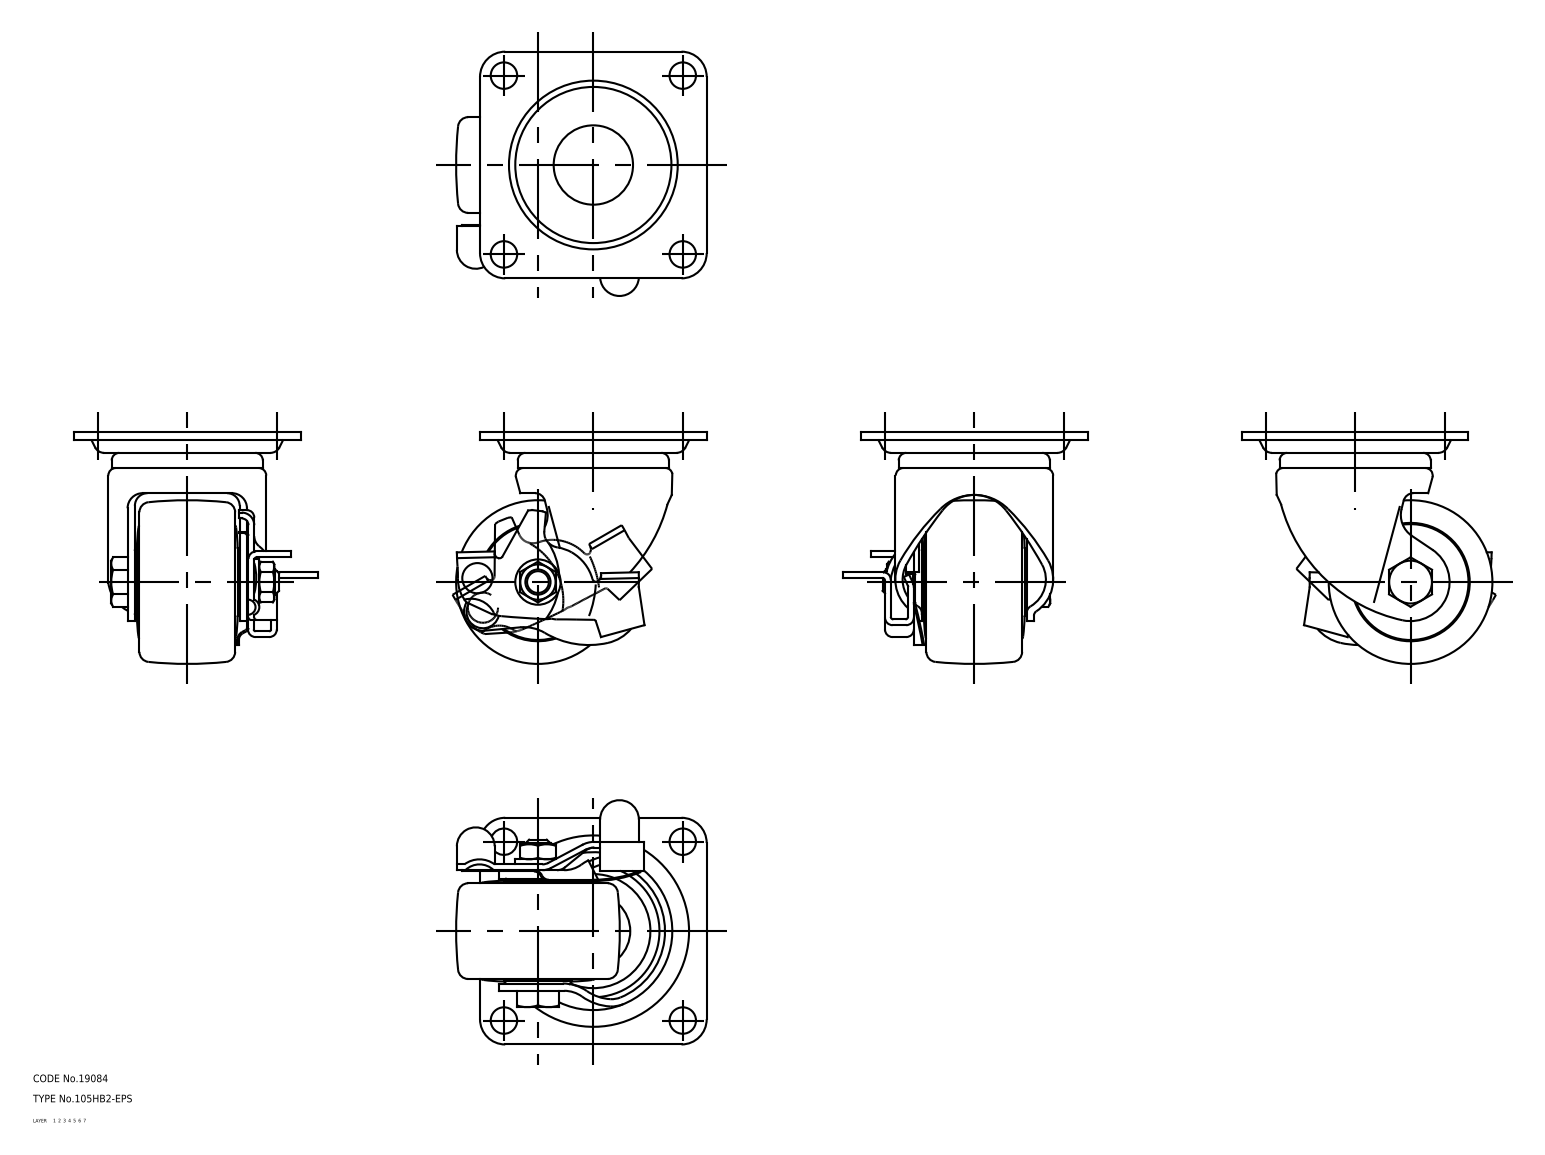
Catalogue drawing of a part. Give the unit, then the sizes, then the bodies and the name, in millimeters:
Units: millimetres
Overall size (bounding box): 99.5 × 97 × 92
Volume: 104 373 mm³ · Surface area: 73 381 mm²
Bodies: 5 solids, 421 faces (0 planar, 0 cylindrical, 421 other)
Part name (STEP PRODUCT): 67135942; 67135955; 67135968; 67135981 (+6 more)
STEP written by: CADfix (AUTOMOTIVE_DESIGN)
